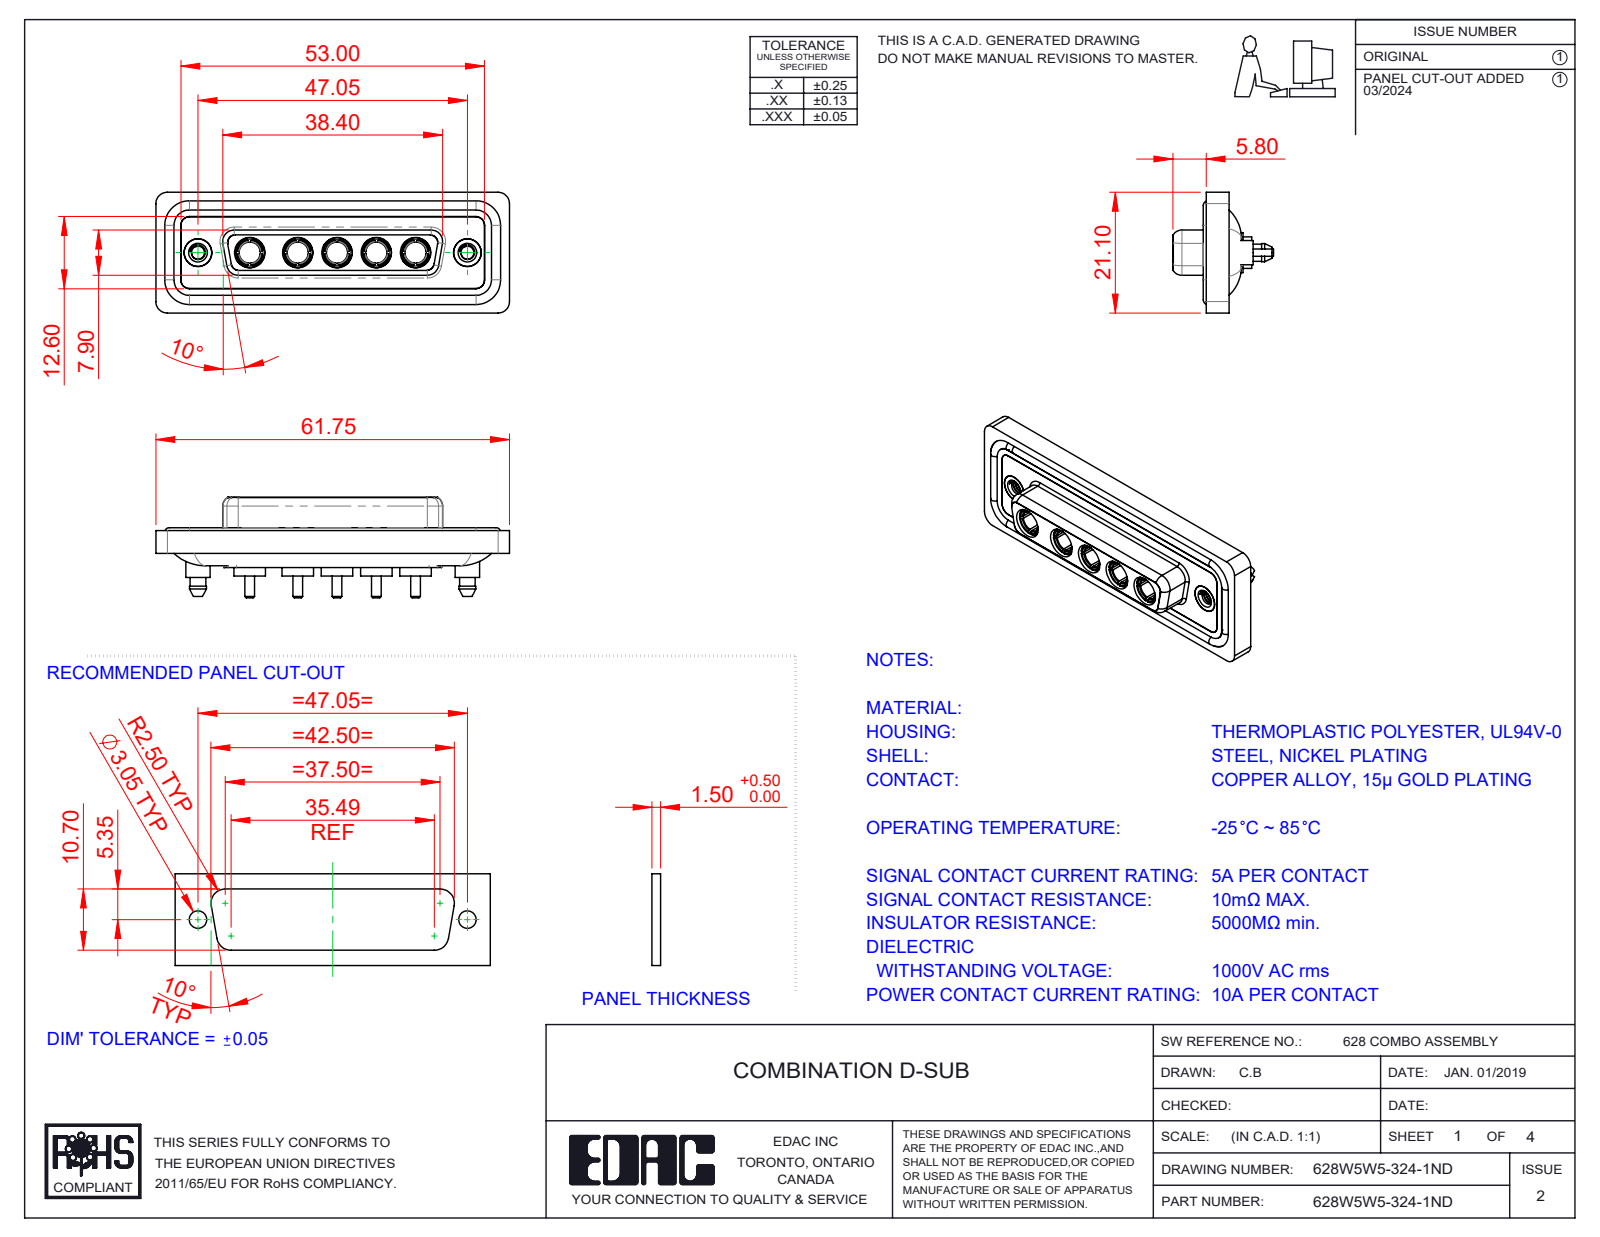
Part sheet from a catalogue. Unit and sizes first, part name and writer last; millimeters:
Units: millimetres
Overall size (bounding box): 61.75 × 21.1 × 17.55
Round holes (diameter × count): ⌀4.85 ×7, ⌀3.7 ×5, ⌀5.3 ×5, ⌀2.26 ×2, ⌀4 ×2, ⌀4.05 ×2, ⌀5 ×2
Round bosses / shafts (diameter × count): ⌀5.5 ×5, ⌀5.2 ×5, ⌀4.96 ×5, ⌀4.75 ×5, ⌀3.75 ×5, ⌀1.7 ×5, ⌀1.6 ×4, ⌀5.4 ×2
Partial cylindrical surfaces — rounded edges, fillets, slot ends (radius × count): R1.5 ×24, R2 ×18, R1.6 ×10, R1.35 ×8, R2.1 ×5, R0.25 ×4, R0.5 ×4, R0.6 ×4
Main face-to-face distances: 0.4, 1.8, 7.45, 5.65, 0.5, 7.05, 6.6, 1.6, 1.1, 1.5
Hole centre spacings: 6.86, 9.04, 13.72, 38.01, 8.39, 15.25, 15.9, 17.43
Volume: 8 235 mm³ · Surface area: 13 692 mm²
Bodies: 17 solids, 822 faces (266 planar, 351 cylindrical, 205 other)
Part name (STEP PRODUCT): Power Socket_10A S; 628Combo Shell Rear_25 Contacts; 628Combo Waterproof Housing_25 Contacts; 628W5W5-324-1ND (+3 more)
STEP written by: SolidWorks 2023 (CONFIG_CONTROL_DESIGN)
